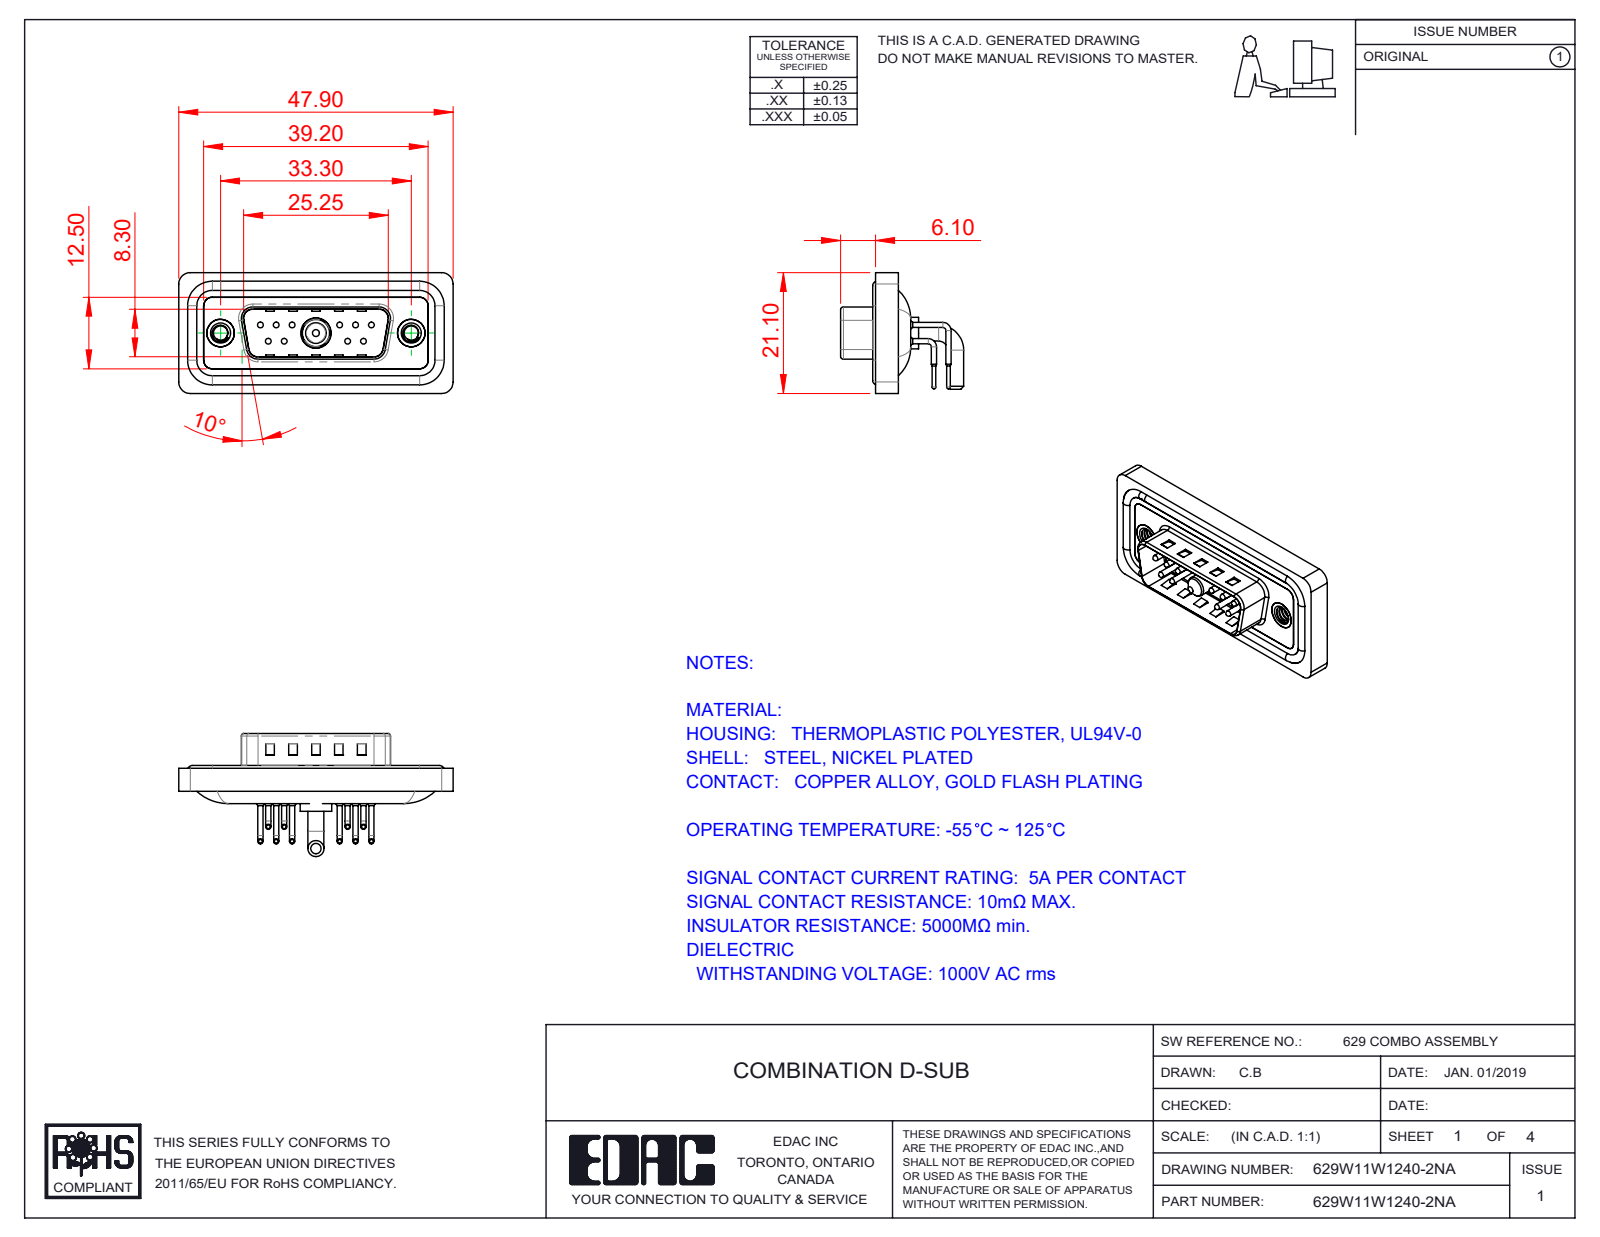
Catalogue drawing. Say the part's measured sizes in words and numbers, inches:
The part is named "629Combo Threaded Rivet_A; 629Combo Shell Rear_15 Contacts; 629Combo Shell Front_15 Contacts; 629Combo Contact Row 1 (+5 more)". Its 3-D file was written by "SolidWorks 2020 (CONFIG_CONTROL_DESIGN)". It is 19 solids with 1597 faces: 836 planar, 567 cylindrical and 194 other. Overall it measures 1.886 by 0.846 by 0.831 inches. Its volume is 0.341 cubic inches and its surface area 14.39 square inches. Round holes: 10 of diameter 0.03, 10 of diameter 0.063, 10 of diameter 0.079, 2 of diameter 0.098, 2 of diameter 0.157, 2 of diameter 0.189, 2 of diameter 0.197, 1 of diameter 0.191, 1 of diameter 0.209. Round bosses or shafts: 20 of diameter 0.035, 10 of diameter 0.059, 10 of diameter 0.039, 10 of diameter 0.026, 4 of diameter 0.063, 2 of diameter 0.193, 2 of diameter 0.11, 1 of diameter 0.217. Partial cylindrical surfaces (rounded edges, fillets, slot ends): 20 of radius 0.079, 18 of radius 0.059, 10 of radius 0.04, 8 of radius 0.02, 8 of radius 0.063, 7 of radius 0.039, 4 of radius 0.01, 4 of radius 0.024. The main face-to-face distances are 0.016, 0.114, 0.031, 0.043, 0.083, 0.063, 0.098, 0.161, 0.177, 0.122. The hole center spacings are 0.124, 0.109, 0.545, 0.436, 0.654, 0.198, 0.198, 0.218.
